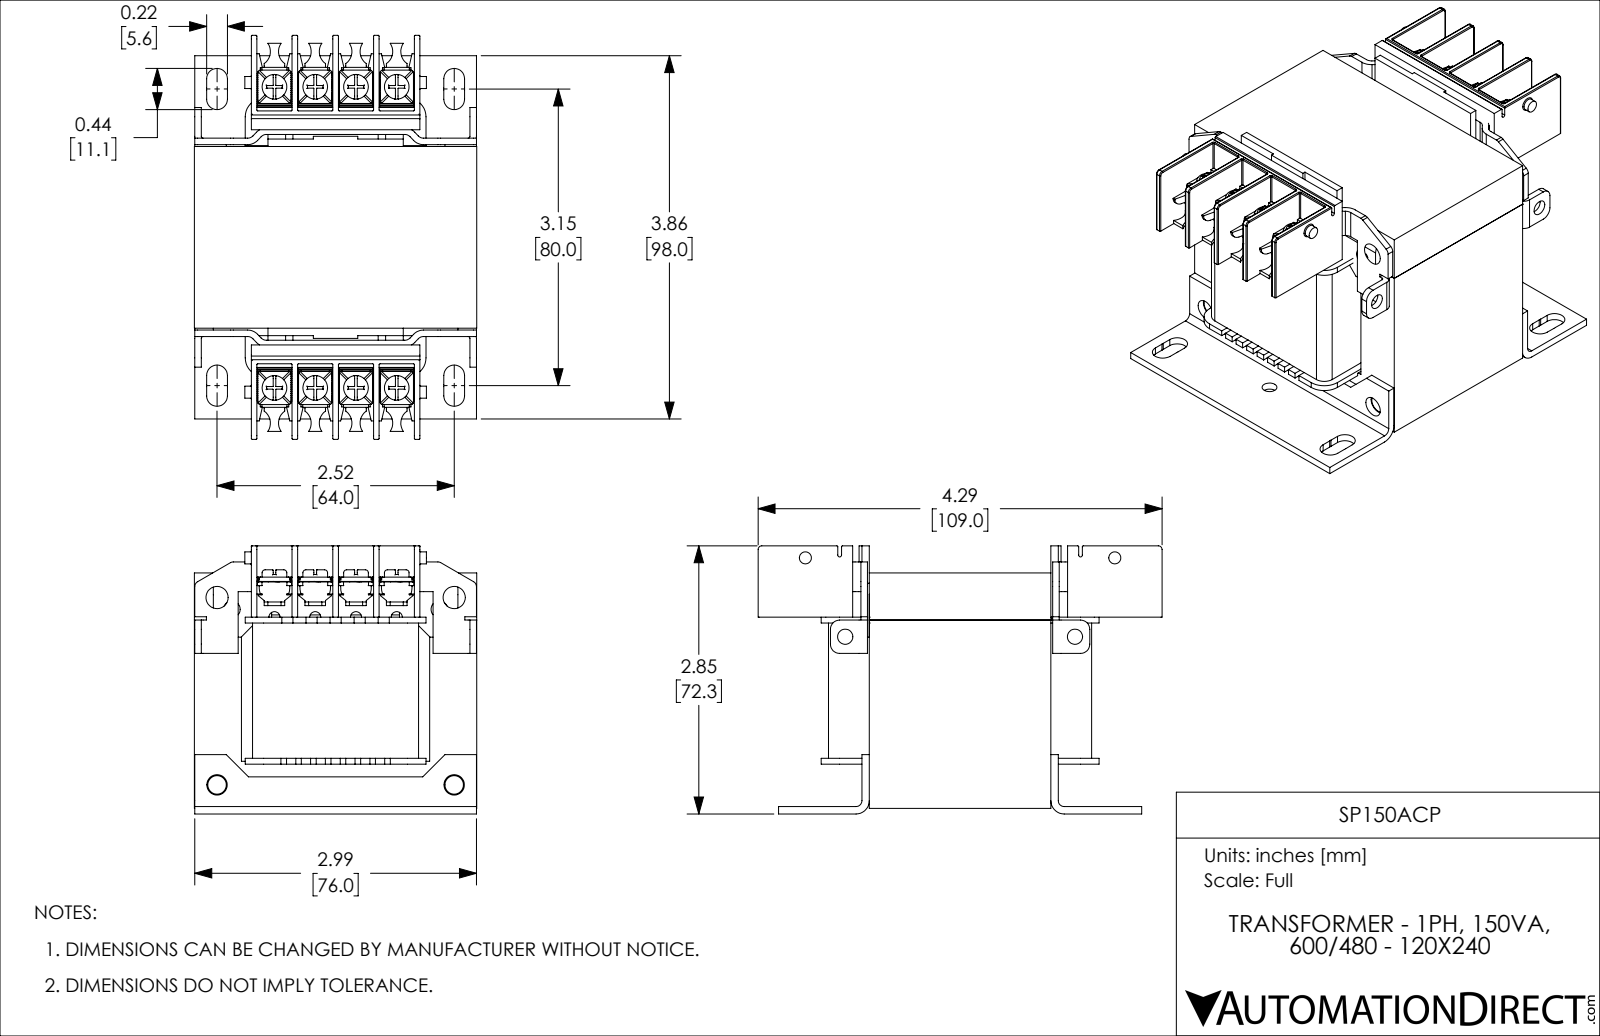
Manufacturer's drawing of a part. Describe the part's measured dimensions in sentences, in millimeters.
The part is named "SP150ACP". Its 3-D file was written by "SolidWorks 2018 (AUTOMOTIVE_DESIGN)". It is 42 solids with 3183 faces: 1948 planar, 941 cylindrical and 294 other. Overall it measures 109 by 76.2 by 72.3 millimeters. Its volume is 301 800 cubic millimeters and its surface area 107 100 square millimeters. Round holes: 10 of diameter 4, 8 of diameter 2.7, 8 of diameter 3.5, 2 of diameter 2.5, 2 of diameter 4.1, 2 of diameter 4.5, 2 of diameter 5, 2 of diameter 5.5, 2 of diameter 6. Round bosses or shafts: 8 of diameter 6.7, 8 of diameter 6.1, 8 of diameter 4.3, 8 of diameter 2.8, 3 of diameter 3.3. Partial cylindrical surfaces (rounded edges, fillets, slot ends): 52 of radius 0.1, 52 of radius 0.3, 46 of radius 0.3, 32 of radius 0.7, 18 of radius 1.5, 16 of radius 4, 12 of radius 0.9, 10 of radius 2. The main face-to-face distances are 12.7, 50.8, 1.5, 11, 2, 63.5, 60.5, 25.4, 49, 38.1. The hole center spacings are 11, 22, 81.7, 33, 80.9, 83.9, 81.5, 81.9.
